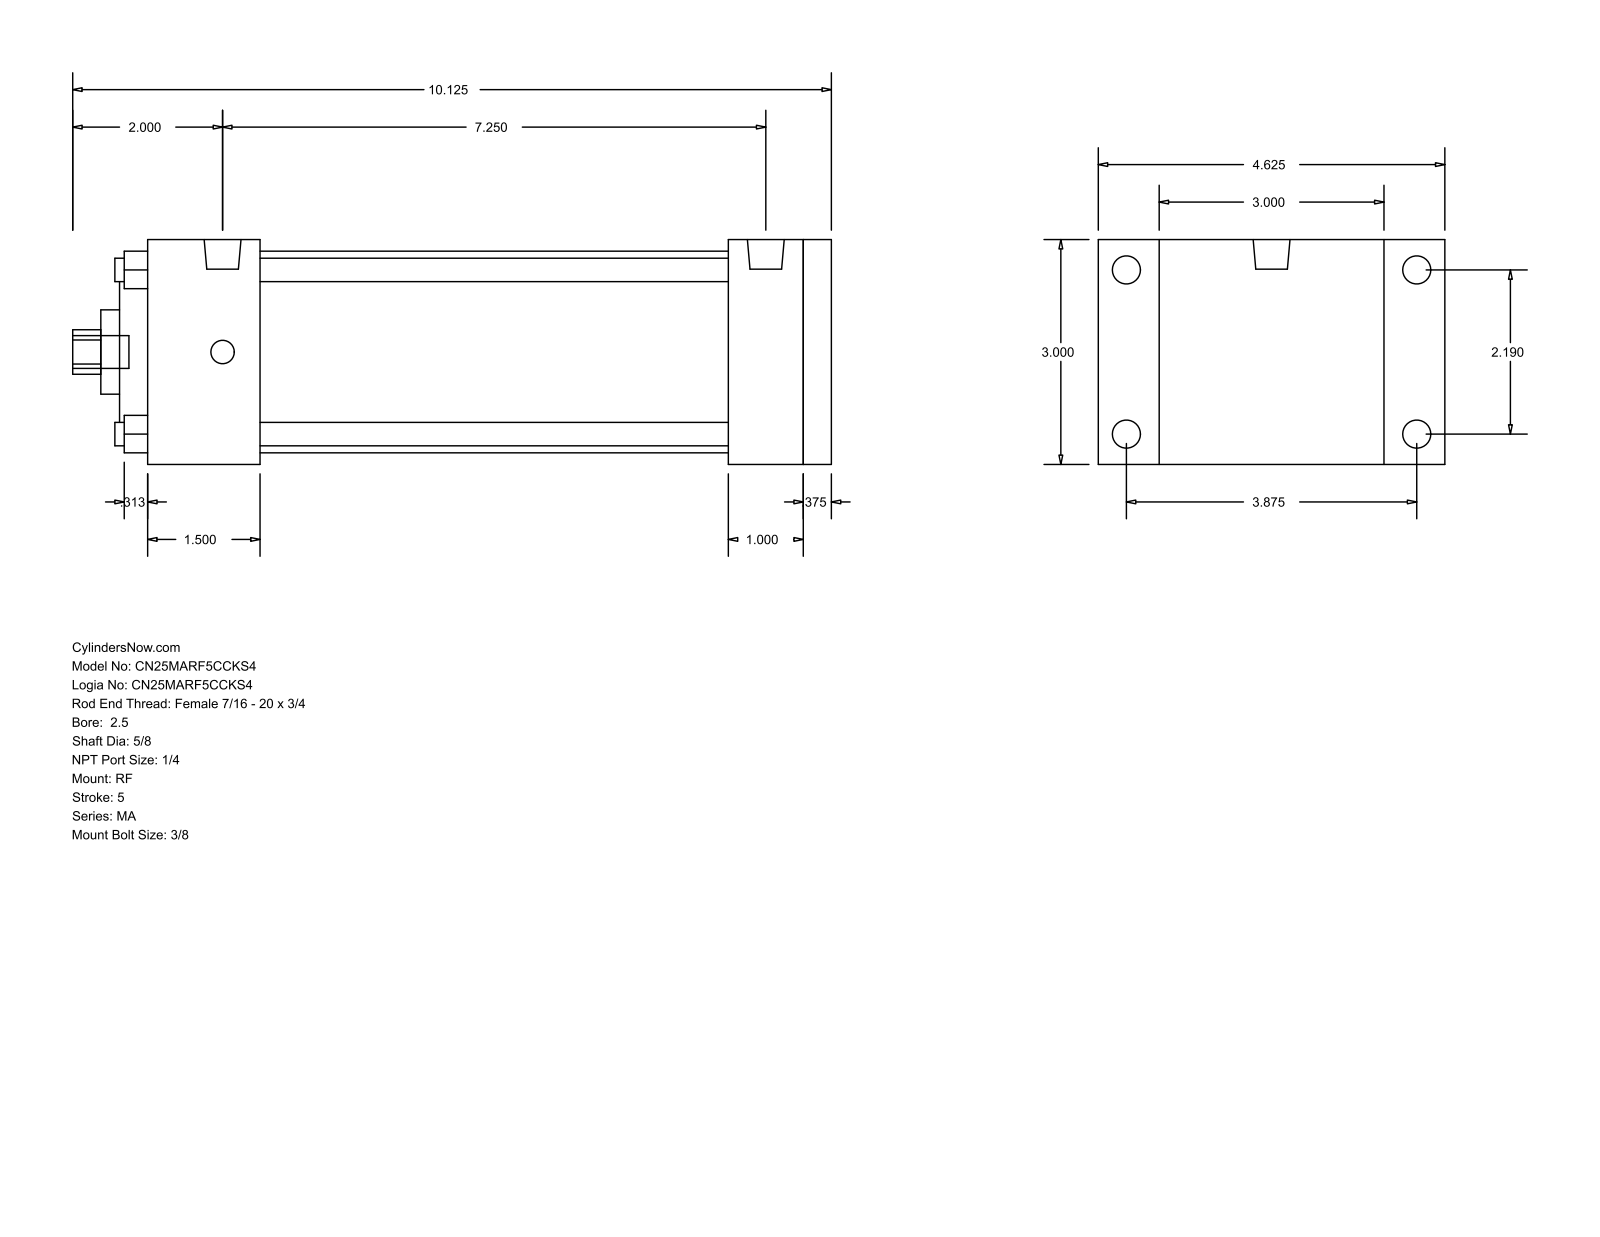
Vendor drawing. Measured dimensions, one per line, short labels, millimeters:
name: MA_RF__0250_0.625
written by: GSSL Pune (CONFIG_CONTROL_DESIGN)
unit: mm
bodies: 0 solids, 94 faces (65 planar, 29 cylindrical, 0 other)
size: 257.18 × 117.47 × 76.2
holes: 4× ⌀7.94, 1× ⌀15.88, 1× ⌀28.57, 1× ⌀50.8, 1× ⌀68.33
bosses: 4× ⌀9.53, 4× ⌀7.94, 2× ⌀12.49, 1× ⌀11.11
rounds: 1× R7.54
face distances: 76.2, 231.78, 9.53, 222.25, 25.4, 38.1, 196.85, 158.75, 184.15, 193.68
hole spacings: 39.33, 55.62, 78.66
